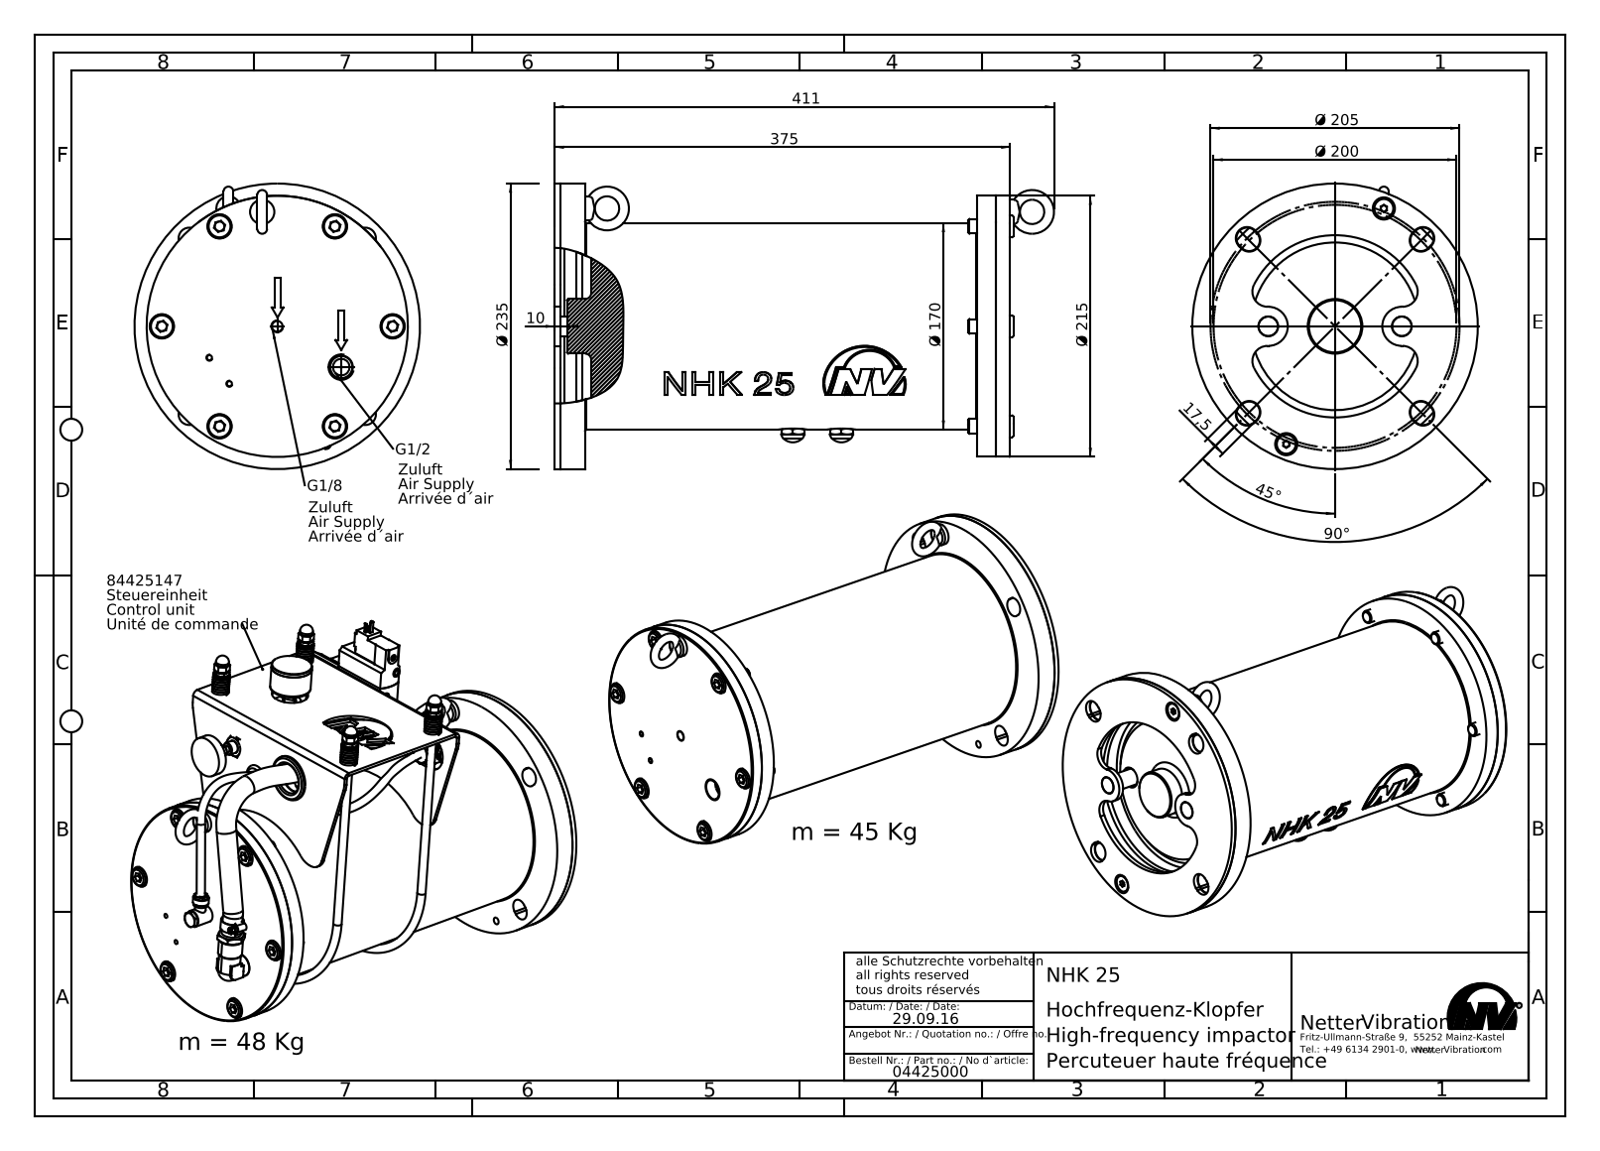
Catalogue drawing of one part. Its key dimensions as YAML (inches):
part_name: "NHK 25 #04425000"
step_written_by: "SolidWorks 2015 (AUTOMOTIVE_DESIGN)"
units: inches
bodies: {solids: 28, faces: 1084, planar: 604, cylindrical: 259, other: 221}
overall_size: [16.417, 9.252, 9.252]
volume: 322.9
surface_area: 1308
round_holes:
  - {diameter: 0.402, count: 6}
  - {diameter: 0.531, count: 6}
  - {diameter: 0.787, count: 6}
  - {diameter: 0.268, count: 3}
  - {diameter: 0.512, count: 3}
  - {diameter: 0.165, count: 2}
  - {diameter: 0.315, count: 2}
  - {diameter: 0.354, count: 2}
  - {diameter: 0.6, count: 2}
  - {diameter: 0.63, count: 2}
  - {diameter: 0.638, count: 2}
  - {diameter: 0.709, count: 2}
round_bosses_or_shafts:
  - {diameter: 0.709, count: 6}
  - {diameter: 0.472, count: 6}
  - {diameter: 0.768, count: 3}
  - {diameter: 0.315, count: 3}
  - {diameter: 0.787, count: 2}
  - {diameter: 0.656, count: 2}
  - {diameter: 0.613, count: 2}
  - {diameter: 0.252, count: 2}
partial_cylinders:
  - {radius: 0.344, count: 8}
  - {radius: 0.364, count: 8}
  - {radius: 0.492, count: 4}
  - {radius: 0.429, count: 2}
  - {radius: 0.634, count: 2}
  - {radius: 2.953, count: 1}
  - {radius: 3.347, count: 1}
face_to_face_distances: [0.197, 0.984, 13.78, 13.583, 0.472, 14.567, 14.764, 6.969, 14.291, 14.094]
hole_center_spacings: [3.74, 6.478, 2.165, 3.252, 5.174, 5.351, 1.575, 7.48]
